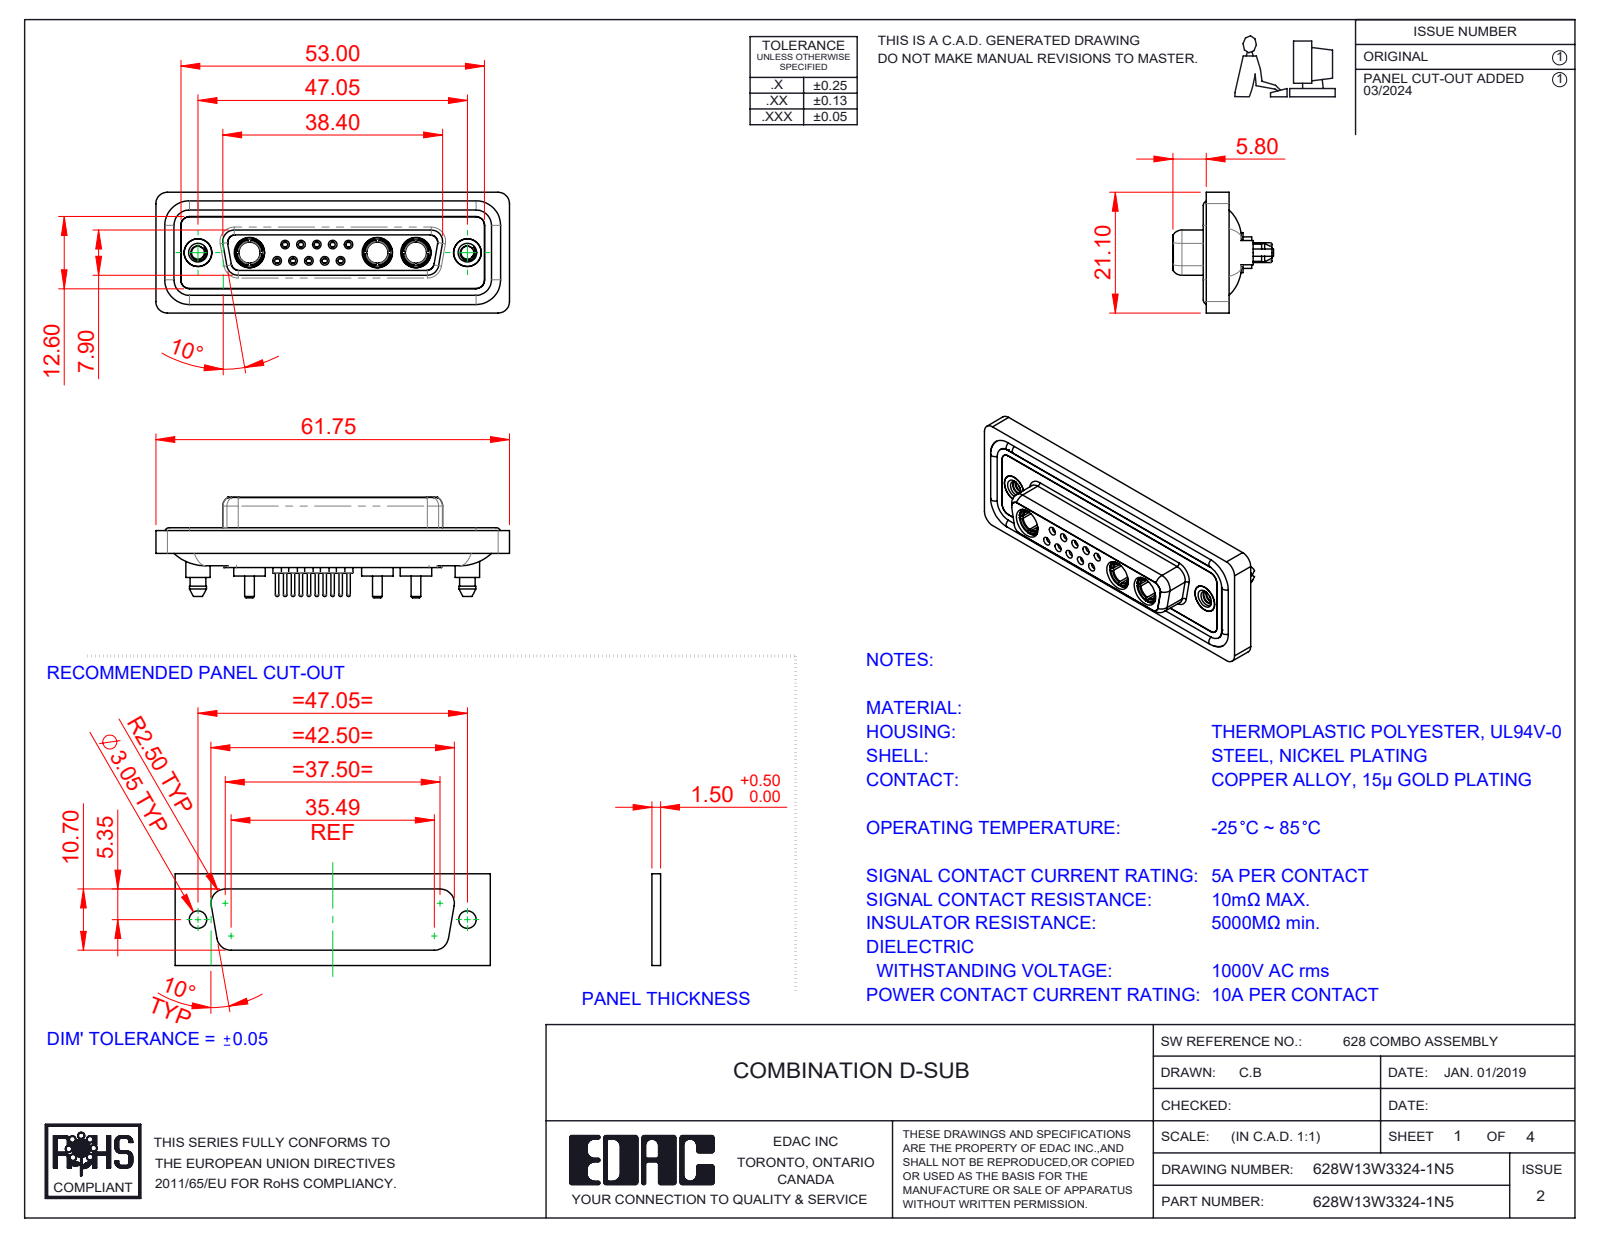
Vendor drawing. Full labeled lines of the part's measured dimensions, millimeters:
Part name (STEP PRODUCT): 628Combo Contact Row 2_24; 628Combo Threaded Boardlock_5; 628Combo Housing_13W3; Power Socket_10A S (+5 more)
STEP written by: SolidWorks 2023 (CONFIG_CONTROL_DESIGN)
Units: millimetres
Bodies: 23 solids, 1208 faces (358 planar, 479 cylindrical, 371 other)
Overall size (bounding box): 61.75 × 21.1 × 17.55
Volume: 8 363 mm³ · Surface area: 14 004 mm²
Round holes (diameter × count): ⌀0.9 ×10, ⌀1.1 ×10, ⌀1.5 ×10, ⌀2 ×10, ⌀1.6 ×5, ⌀1.7 ×5, ⌀4.85 ×5, ⌀3.7 ×3, ⌀5.3 ×3, ⌀2.26 ×2, ⌀4 ×2, ⌀4.05 ×2
Round bosses / shafts (diameter × count): ⌀2.2 ×10, ⌀0.6 ×10, ⌀1.6 ×9, ⌀5.5 ×3, ⌀5.2 ×3, ⌀4.96 ×3, ⌀4.75 ×3, ⌀3.75 ×3
Partial cylindrical surfaces — rounded edges, fillets, slot ends (radius × count): R1.5 ×24, R2 ×18, R1.6 ×10, R1.35 ×8, R0.25 ×4, R0.5 ×4, R0.6 ×4, R0.65 ×4
Main face-to-face distances: 0.4, 1.8, 7.45, 5.65, 0.5, 6.6, 7.05, 1.6, 2.9, 1.1
Hole centre spacings: 3.16, 2.77, 5.03, 5.04, 5.54, 8.31, 7.49, 2.76
